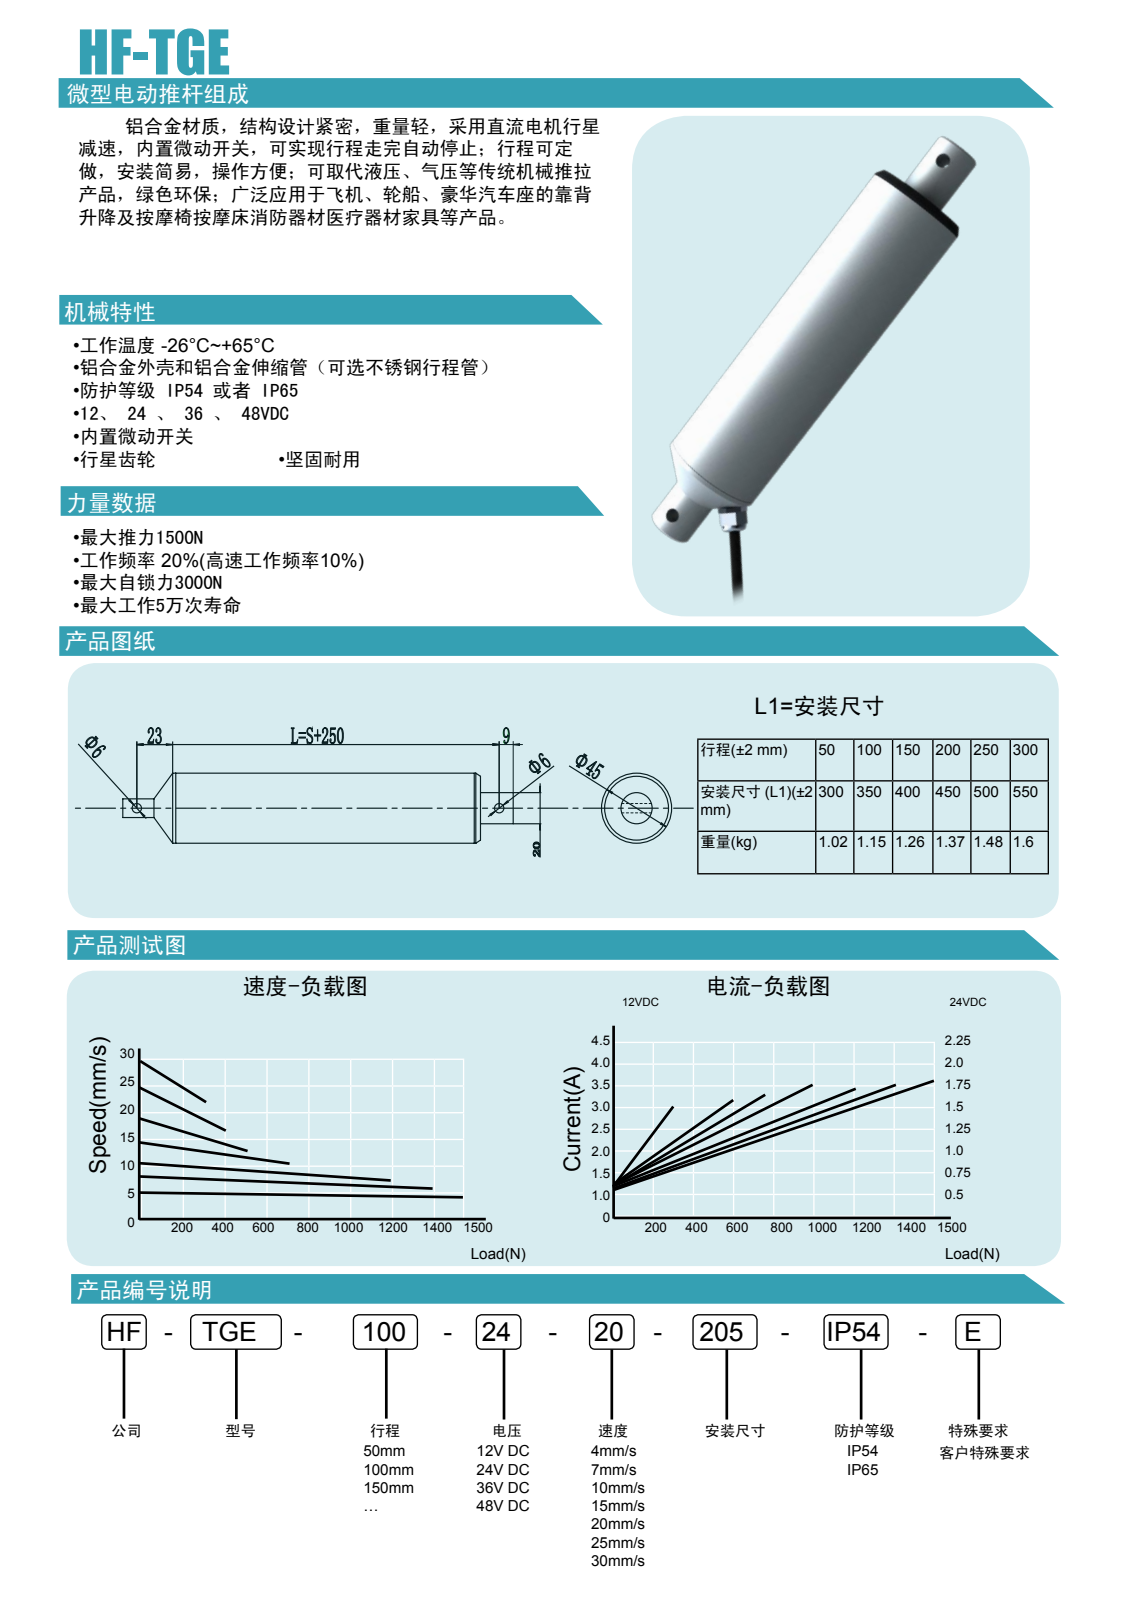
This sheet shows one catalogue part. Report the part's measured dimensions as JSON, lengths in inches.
{"part_name": "WK; FENGTOU; NG; HOUGAI (+1 more)", "step_written_by": "PRO/ENGINEER BY PARAMETRIC TECHNOLOGY CORPORATION, 2008380 (CONFIG_CONTROL_DESIGN)", "units": "inches", "bodies": {"solids": 4, "faces": 48, "planar": 8, "cylindrical": 18, "other": 22}, "overall_size": [14.528, 1.772, 1.772], "volume_in3": 34.69, "surface_area_in2": 103.7, "round_holes": [[0.118, 2], [0.252, 2]], "round_bosses_or_shafts": [[1.772, 1], [0.787, 1]], "face_to_face_distances": [12.323, 12.441, 0.118, 7.205, 13.228, 5.118, 5.236, 6.024, 0.906, 0.787], "hole_center_spacings": [1.26, 13.78]}
